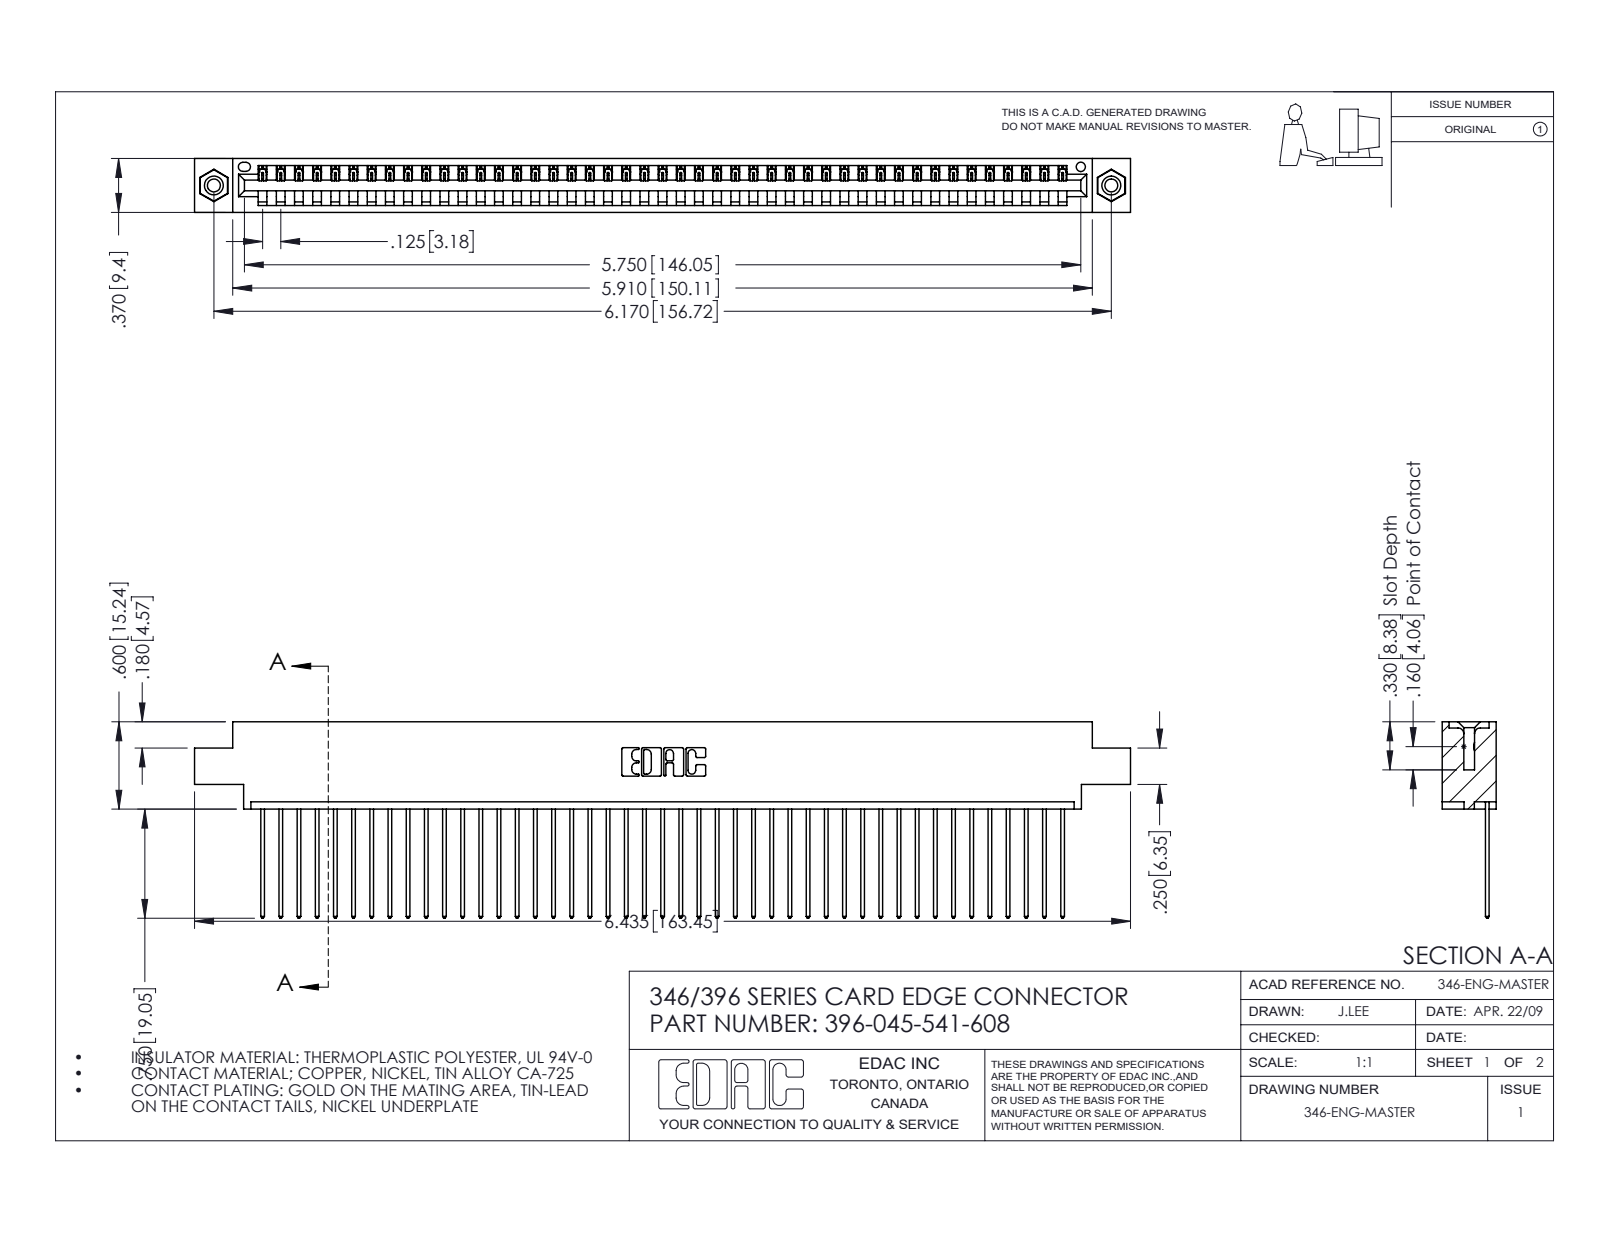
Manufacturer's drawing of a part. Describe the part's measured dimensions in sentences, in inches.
The part is named "345-292-001_345-293-141; 345-250-001_345-250-003-102; 396-045-541-608; 346 Part_0.170 Offset - 0.156 Dia-TI". Its 3-D file was written by "SolidWorks 2016 (CONFIG_CONTROL_DESIGN)". It is 48 solids with 2796 faces: 1912 planar, 868 cylindrical and 16 other. Overall it measures 6.435 by 1.35 by 0.37 inches. Its volume is 0.955 cubic inches and its surface area 32.03 square inches. Round holes: 2 of diameter 0.089, 2 of diameter 0.125, 2 of diameter 0.156, 1 of diameter 0.064. Round bosses or shafts: 2 of diameter 0.155. Partial cylindrical surfaces (rounded edges, fillets, slot ends): 90 of radius 0.006, 90 of radius 0.01, 22 of radius 0.01, 6 of radius 0.007, 6 of radius 0.031, 3 of radius 0.026, 2 of radius 0.031, 2 of radius 0.04. The main face-to-face distances are 0.048, 0.322, 0.37, 0.25, 0.072, 0.298, 0.025, 0.222, 0.148, 0.1. The hole center spacings are 0.246, 5.961, 6.17.
